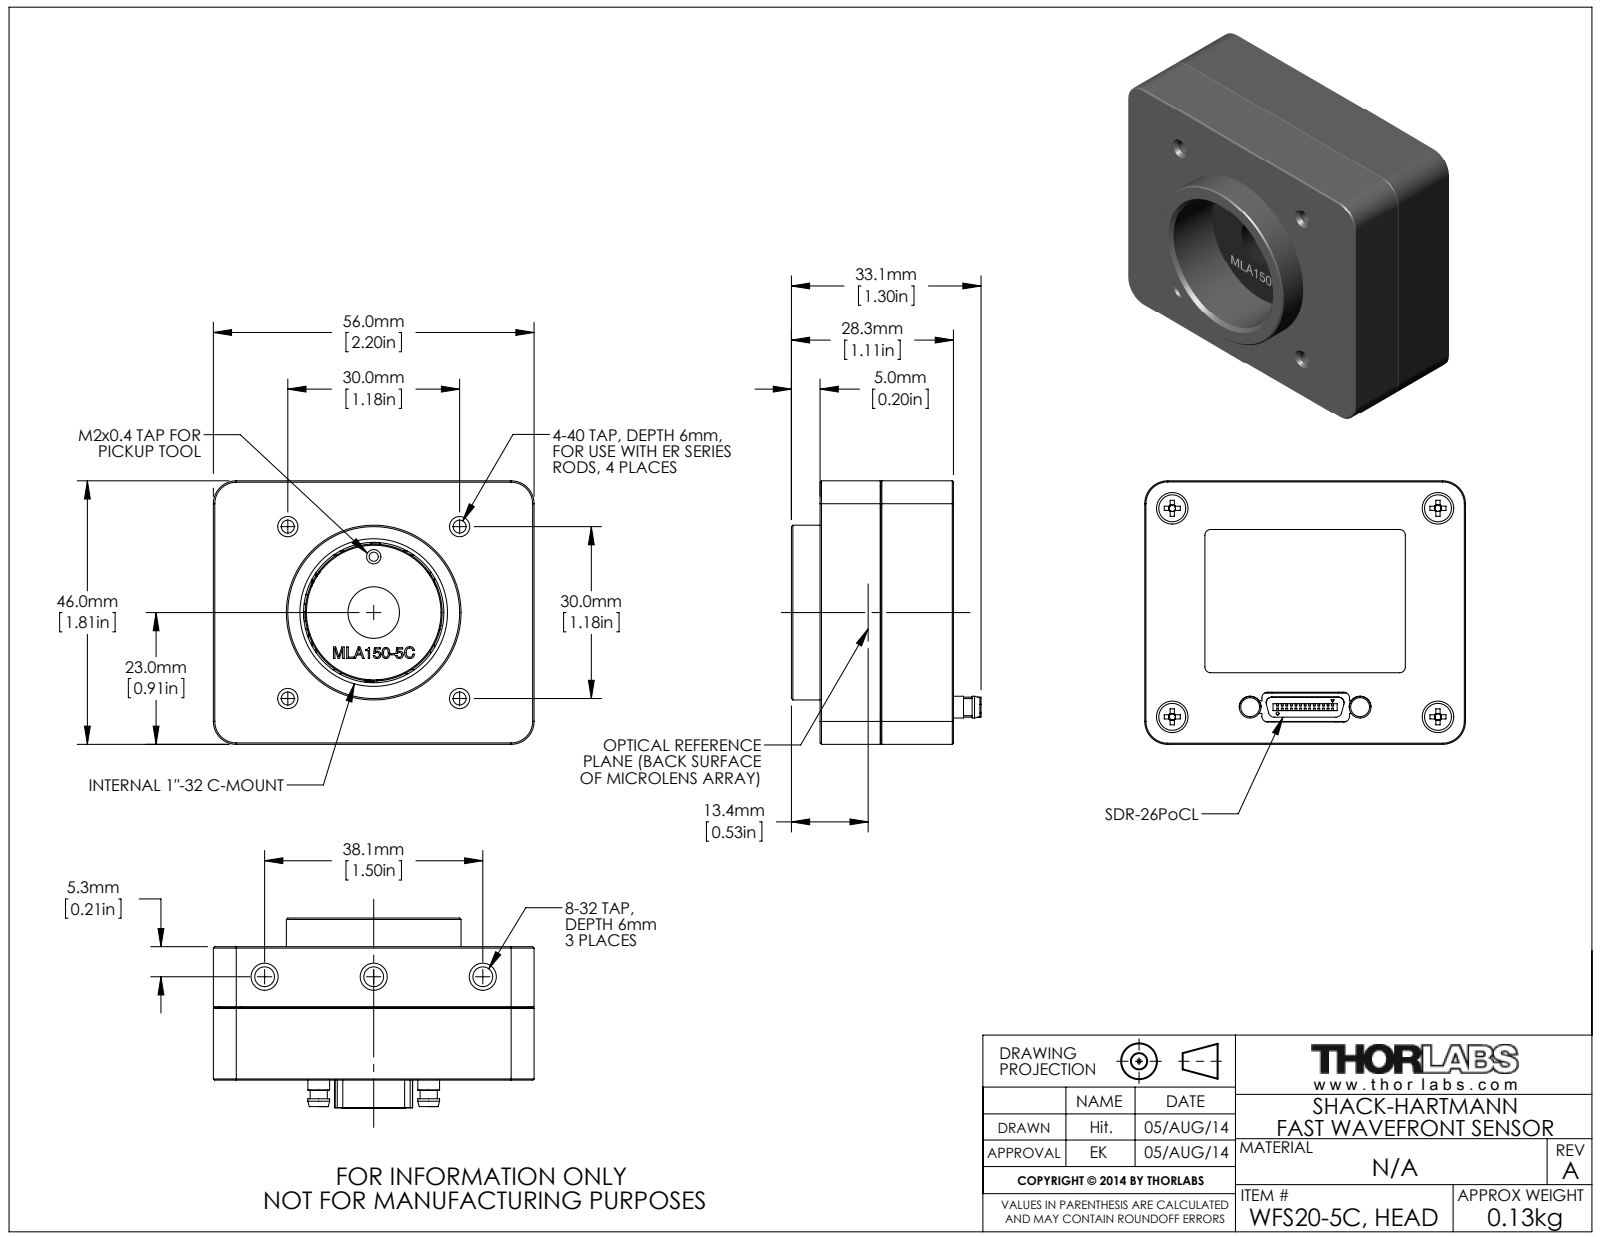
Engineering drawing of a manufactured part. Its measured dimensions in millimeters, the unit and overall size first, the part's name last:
Units: millimetres
Overall size (bounding box): 56 × 46 × 33.11
Round holes (diameter × count): ⌀0.6 ×26, ⌀3.2 ×6, ⌀2.05 ×4, ⌀2.26 ×4, ⌀2.7 ×4, ⌀2.9 ×4, ⌀3 ×4, ⌀6 ×4, ⌀1.9 ×3, ⌀3.45 ×3, ⌀1.2 ×2, ⌀1.75 ×2
Round bosses / shafts (diameter × count): ⌀0.7 ×108, ⌀1 ×11, ⌀3 ×8, ⌀5.6 ×4, ⌀4.7 ×4, ⌀2.5 ×4, ⌀2.1 ×4, ⌀3.8 ×2
Partial cylindrical surfaces — rounded edges, fillets, slot ends (radius × count): R1 ×19, R2 ×12, R0.18 ×6, R0.2 ×4, R2.75 ×4, R3.1 ×4, R3.5 ×4, R3.8 ×4
Main face-to-face distances: 14.98, 16.59, 1.61, 3.5, 19.39, 3.9, 13.5, 1.48, 3.09, 1
Hole centre spacings: 1.4, 1.6, 2.66, 5.72, 3.2, 3.5, 4.16, 4.46
Volume: 71 638 mm³ · Surface area: 44 250 mm²
Bodies: 51 solids, 2410 faces (1141 planar, 687 cylindrical, 582 other)
Part name (STEP PRODUCT): Linsenarray; Halter Teil1 WFS20; Halter Teil2; MTN003815 (+8 more)
STEP written by: SolidWorks 2014 (AUTOMOTIVE_DESIGN)
